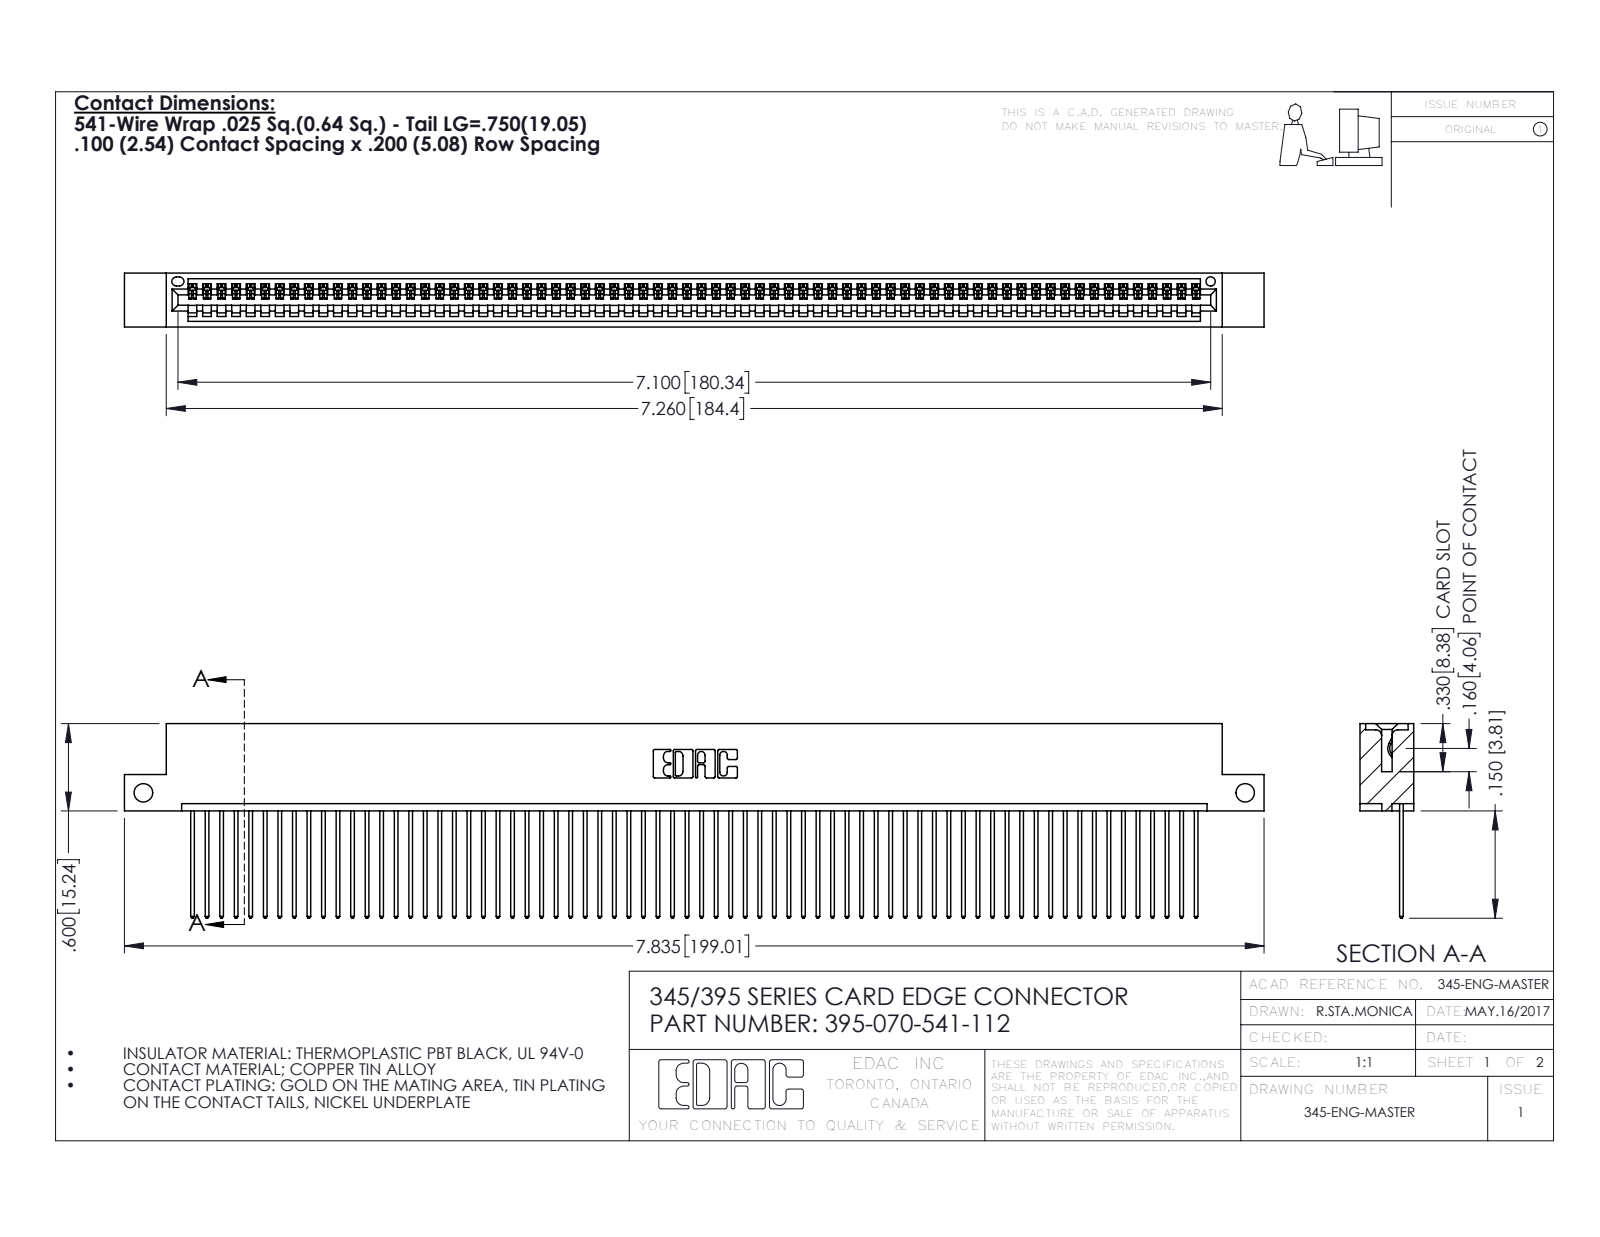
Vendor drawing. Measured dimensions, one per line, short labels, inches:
name: 345-292-001_345-293-141; 395-070-541-112; 345 Part_Flush Mounting Lugs - Side Mount
written by: SolidWorks 2016 (CONFIG_CONTROL_DESIGN)
unit: in
bodies: 71 solids, 4186 faces (2880 planar, 1306 cylindrical, 0 other)
size: 7.835 × 1.337 × 0.37
volume: 1.176 in³; area: 42.18 in²
holes: 2× ⌀0.128, 1× ⌀0.064
rounds: 140× R0.006, 140× R0.01, 22× R0.01, 6× R0.007, 6× R0.031, 3× R0.026, 2× R0.031, 2× R0.04
face distances: 0.072, 0.298, 0.098, 0.272, 0.025, 0.37, 0.2, 0.225, 0.149, 0.072
hole spacings: 7.575
